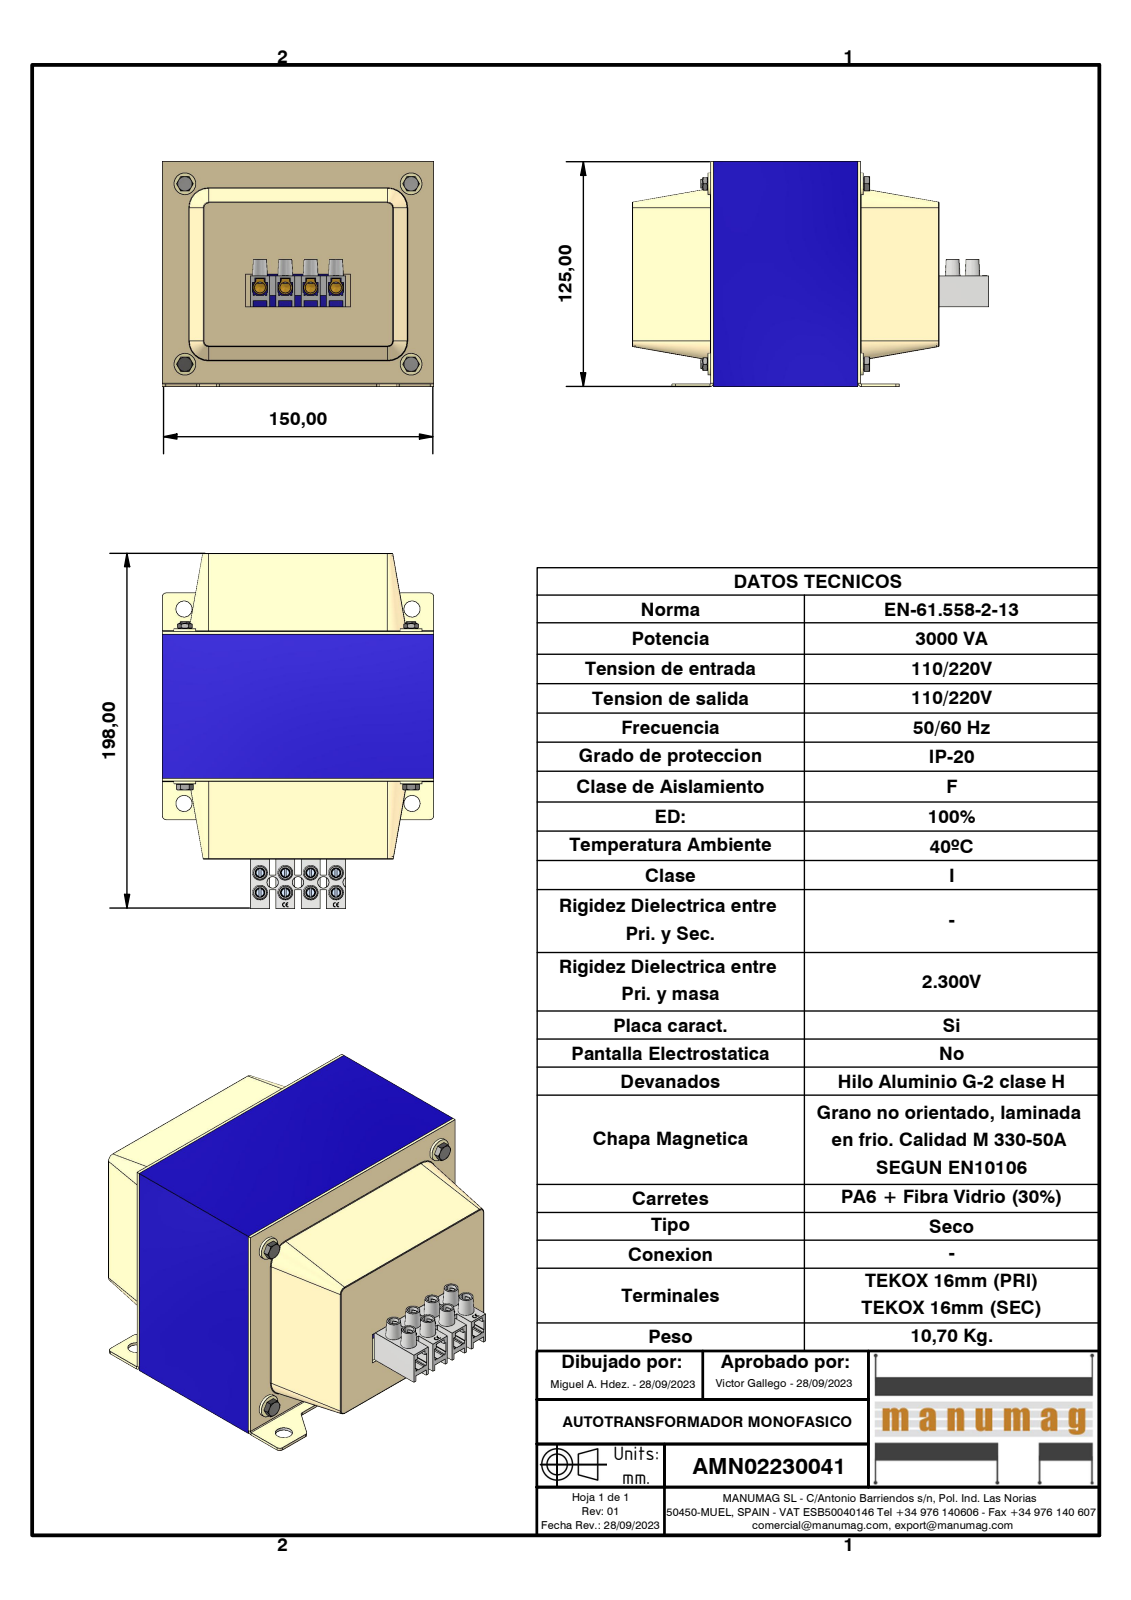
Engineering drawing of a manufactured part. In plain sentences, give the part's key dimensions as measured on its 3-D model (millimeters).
The part is named "AMN02230041; EI150 x 125 - 80 (RC50) Azul; TAPA RC50 CIEGA; TAPA RC50 VENTANA 4 ELEMENTOS 16 (+8 more)". Its 3-D file was written by "Autodesk Inventor 2023 (AUTOMOTIVE_DESIGN)". It is 40 solids with 1665 faces: 1108 planar, 230 cylindrical and 327 other. Overall it measures 197.5 by 150 by 125 millimeters. Its volume is 1 265 000 cubic millimeters and its surface area 282 864 square millimeters. Round holes: 12 of diameter 3.24, 8 of diameter 5.5, 8 of diameter 6, 4 of diameter 5, 4 of diameter 8, 4 of diameter 9, 3 of diameter 6.3. Round bosses or shafts: 8 of diameter 4, 4 of diameter 12, 4 of diameter 6.7, 4 of diameter 5.9, 4 of diameter 4.57. Partial cylindrical surfaces (rounded edges, fillets, slot ends): 16 of radius 0.38, 16 of radius 2.75, 14 of radius 2, 8 of radius 0.82, 8 of radius 3, 6 of radius 0.22, 4 of radius 0.1, 4 of radius 0.81. The main face-to-face distances are 125, 1.5, 25, 43.5, 100, 80, 123.5, 50, 108.12, 42. The hole center spacings are 14, 28, 8.8, 9, 17.8, 11, 21.67, 21.75.
